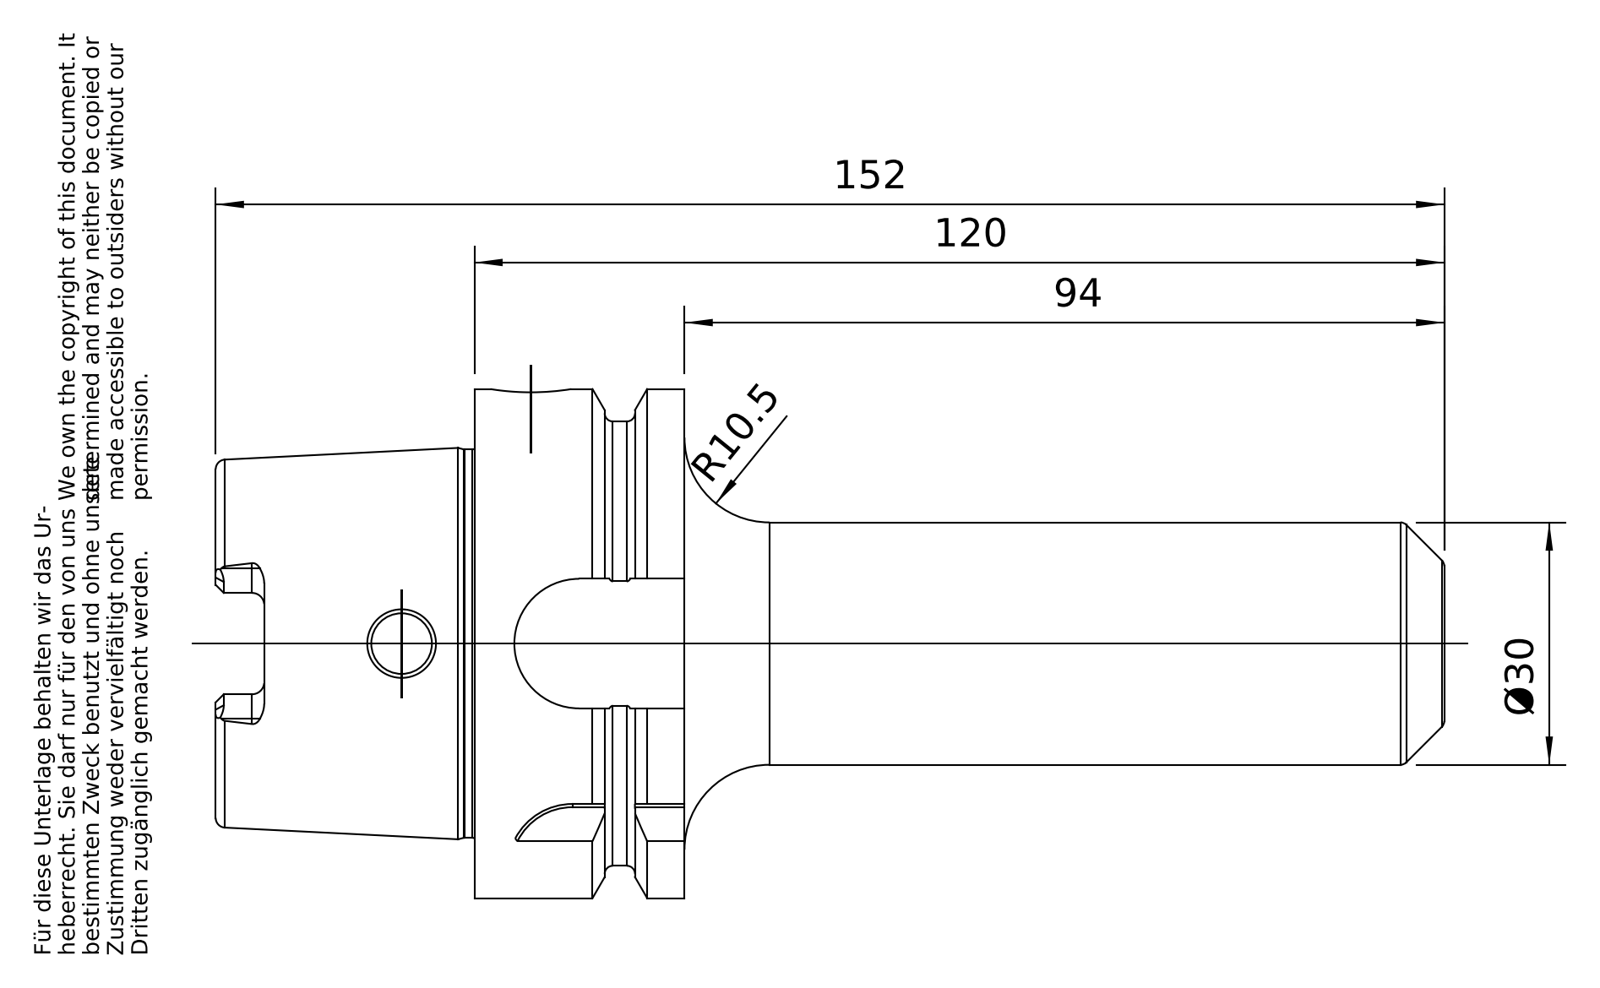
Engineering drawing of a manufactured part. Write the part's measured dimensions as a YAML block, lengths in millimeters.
part_name: "A63-120-01"
step_written_by: "PRO/ENGINEER BY PARAMETRIC TECHNOLOGY CORPORATION, 2010430 (CONFIG_CONTROL_DESIGN)"
units: millimeters
bodies: {solids: 1, faces: 177, planar: 57, cylindrical: 48, other: 72}
overall_size: [152, 63, 63]
volume: 141319
surface_area: 33112
round_holes:
  - {diameter: 7.5, count: 1}
  - {diameter: 10, count: 1}
  - {diameter: 13.72, count: 1}
  - {diameter: 16.92, count: 1}
  - {diameter: 18.32, count: 1}
  - {diameter: 18.66, count: 1}
  - {diameter: 34, count: 1}
  - {diameter: 40, count: 1}
round_bosses_or_shafts:
  - {diameter: 63, count: 1}
  - {diameter: 55, count: 1}
  - {diameter: 48.04, count: 1}
  - {diameter: 30, count: 1}
  - {diameter: 18, count: 1}
partial_cylinders:
  - {radius: 1.5, count: 6}
  - {radius: 3, count: 4}
  - {radius: 8, count: 1}
  - {radius: 8.02, count: 1}
  - {radius: 9.02, count: 1}
face_to_face_distances: [26, 10, 16, 32, 42, 58, 52.8, 53.8, 21.8, 11.8]
